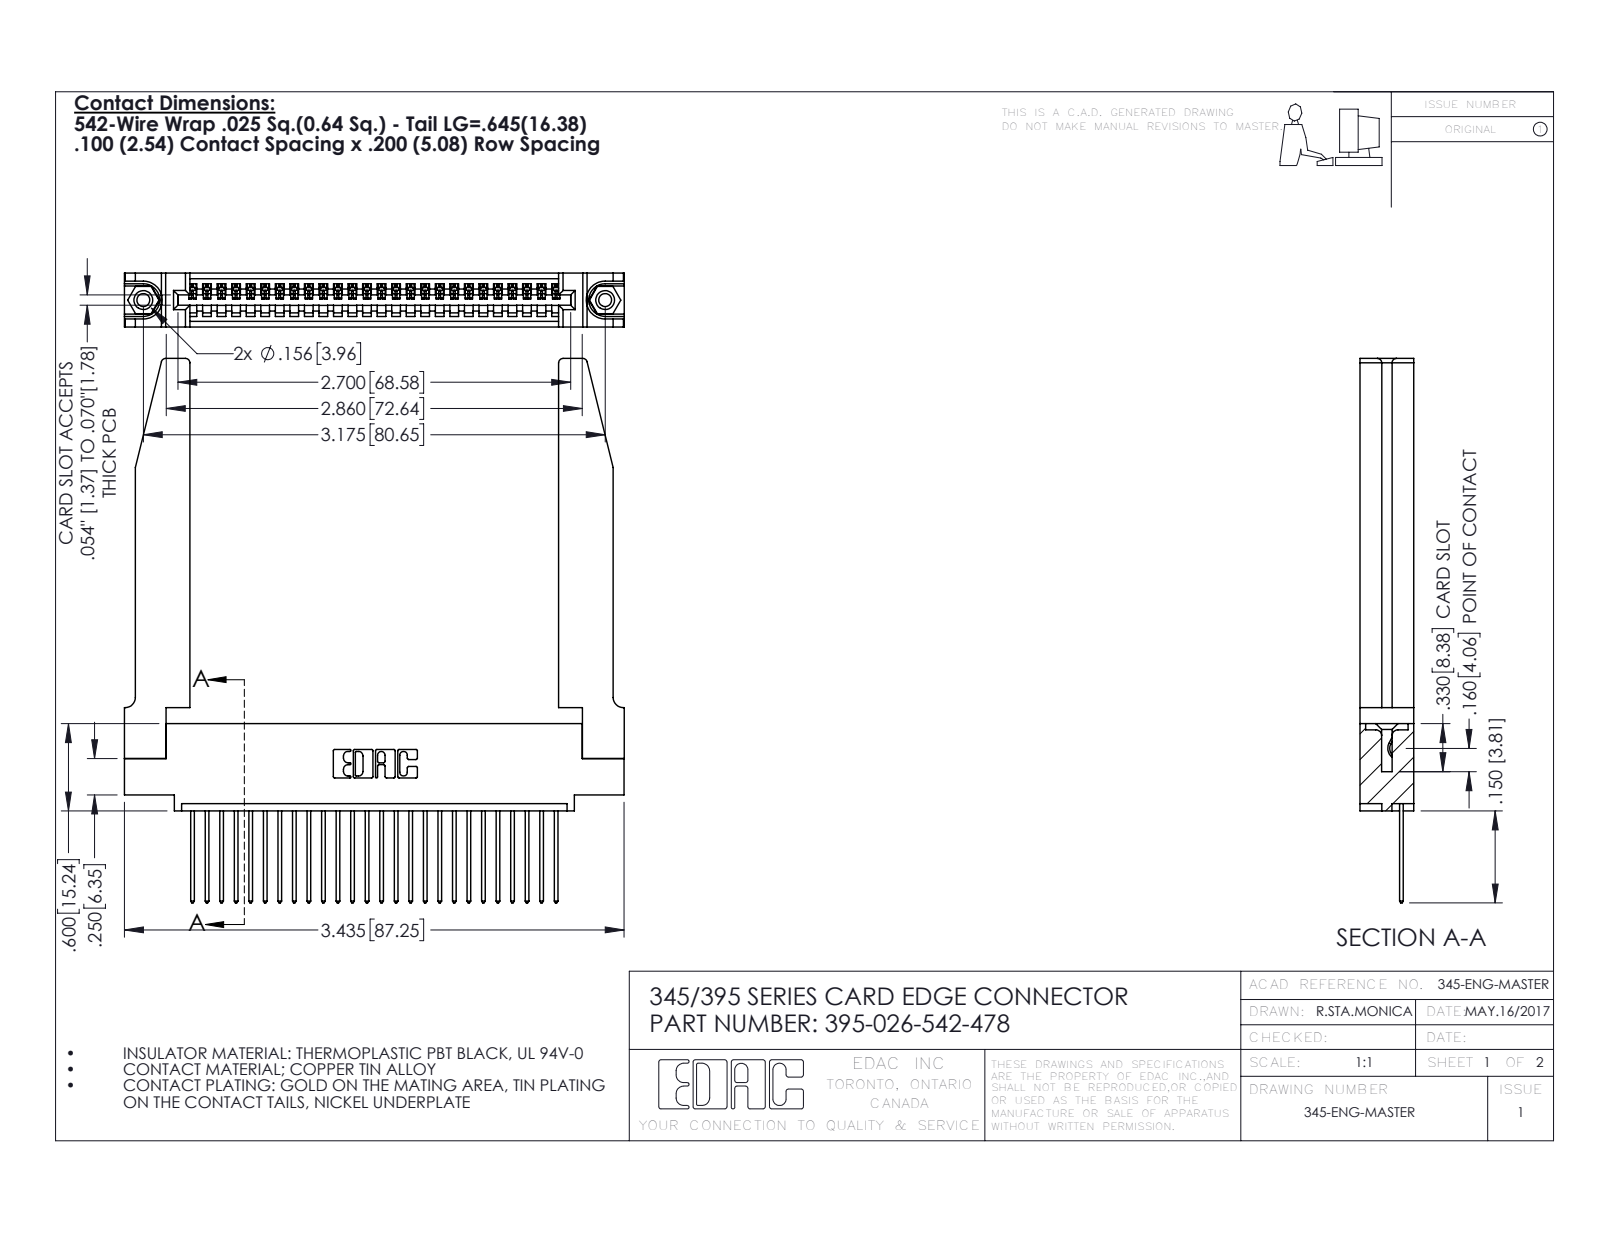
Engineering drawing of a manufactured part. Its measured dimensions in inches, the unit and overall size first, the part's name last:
Units: inches
Overall size (bounding box): 3.742 × 3.436 × 0.37
Round holes (diameter × count): ⌀0.089 ×2, ⌀0.125 ×2, ⌀0.156 ×2, ⌀0.064 ×1
Round bosses / shafts (diameter × count): ⌀0.155 ×2
Partial cylindrical surfaces — rounded edges, fillets, slot ends (radius × count): R0.006 ×52, R0.01 ×52, R0.01 ×22, R0.03 ×8, R0.007 ×6, R0.031 ×6, R0.026 ×3, R0.031 ×2
Main face-to-face distances: 0.37, 0.072, 0.298, 0.098, 0.272, 0.025, 0.2, 0.148, 0.15, 0.225
Hole centre spacings: 0.27, 2.94, 3.175
Volume: 0.971 in³ · Surface area: 27.74 in²
Bodies: 31 solids, 1872 faces (1266 planar, 554 cylindrical, 52 other)
Part name (STEP PRODUCT): 345-220-078_345-220-078; 345-250-001_345-250-001-102; 395-026-542-478; 345-292-001_345-293-142 (+1 more)
STEP written by: SolidWorks 2016 (CONFIG_CONTROL_DESIGN)
